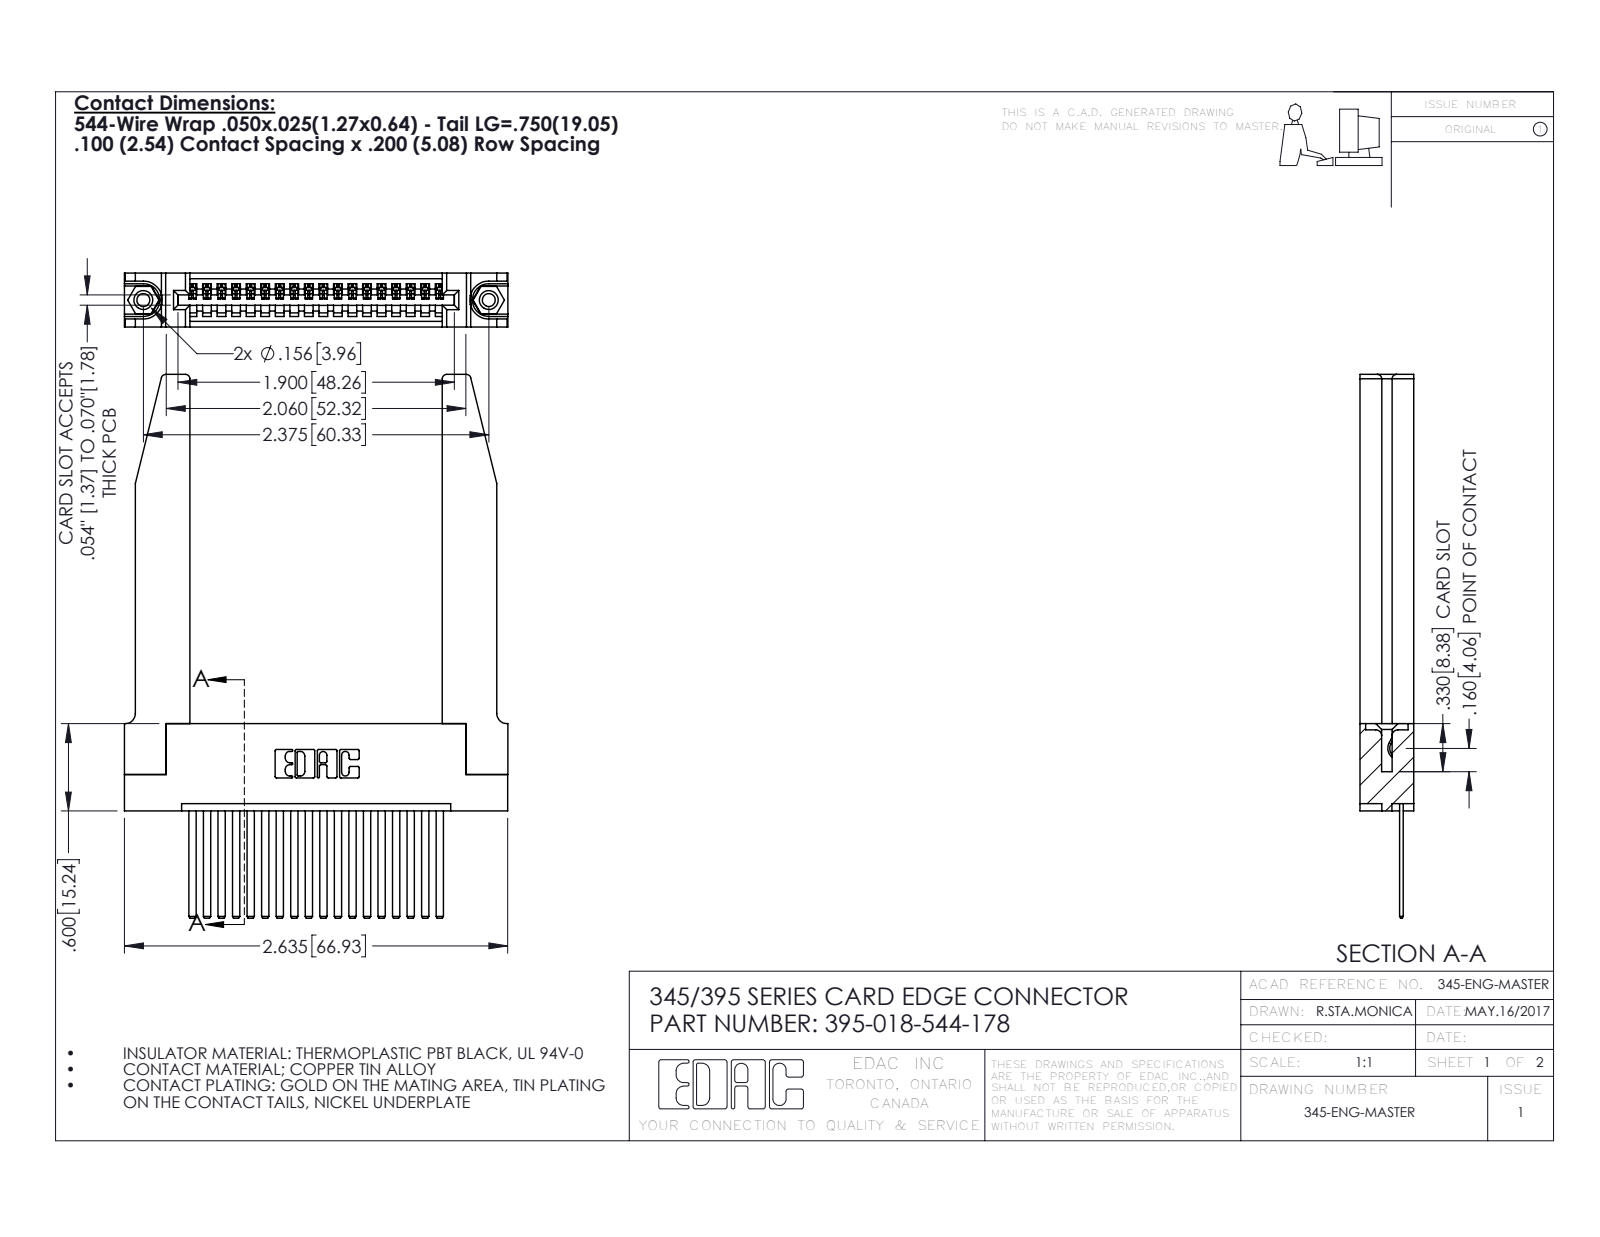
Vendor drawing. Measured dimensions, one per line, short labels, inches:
name: 345-292-001_345-293-144; 345 Part_Flush Mounting Lugs - 0.156 Dia-TH; 345-220-078_345-220-078; 395-018-544-178 (+1 more)
written by: SolidWorks 2016 (CONFIG_CONTROL_DESIGN)
unit: in
bodies: 23 solids, 1296 faces (870 planar, 374 cylindrical, 52 other)
size: 3.737 × 2.636 × 0.37
volume: 0.863 in³; area: 24.2 in²
holes: 2× ⌀0.089, 2× ⌀0.125, 2× ⌀0.156, 1× ⌀0.064
bosses: 2× ⌀0.155
rounds: 36× R0.006, 22× R0.01, 8× R0.03, 6× R0.007, 6× R0.031, 3× R0.026, 2× R0.031, 2× R0.04
face distances: 0.37, 0.072, 0.298, 0.098, 0.272, 0.025, 0.2, 0.15, 0.148, 0.077
hole spacings: 0.27, 2.141, 2.375
